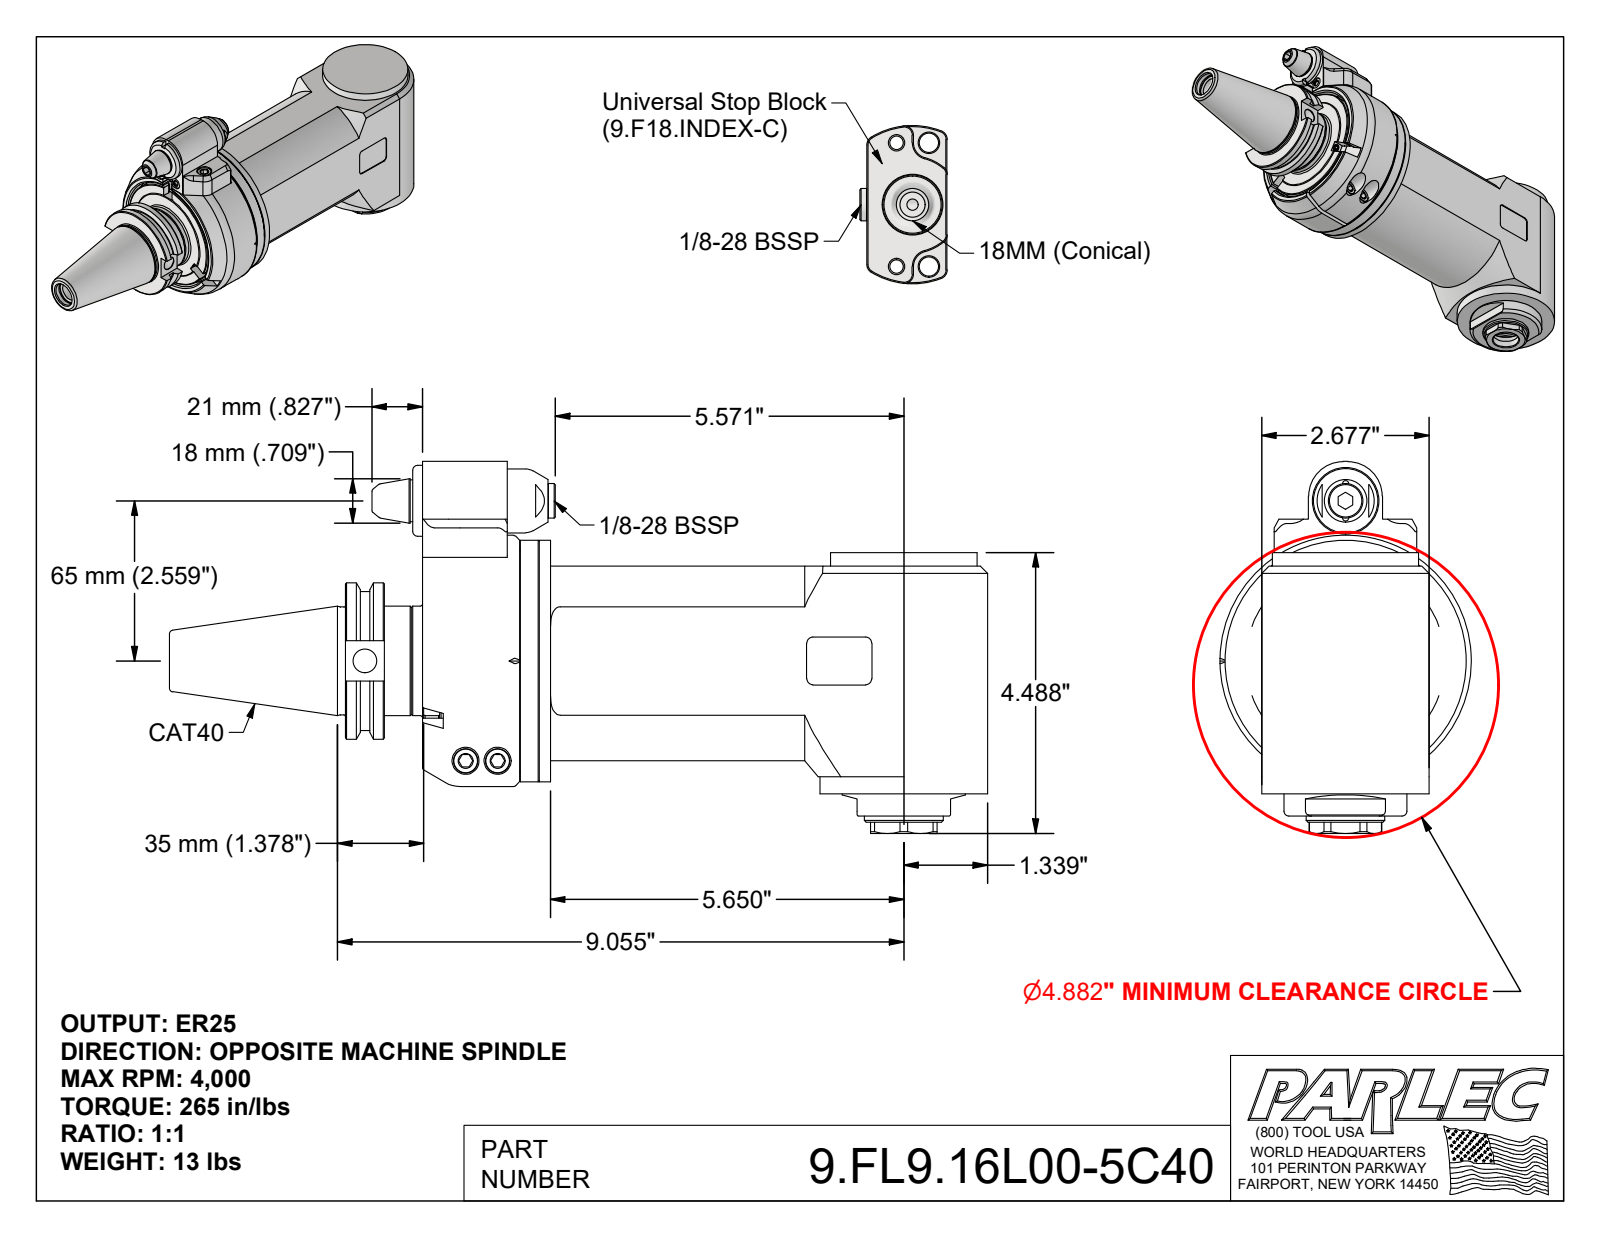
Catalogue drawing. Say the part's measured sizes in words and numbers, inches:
The part is named "9.FL9.16L00-5C40; 9_GA15C_446 (EVO, Type 1, Cat40, 65mm, conical); 9FA636000; VTCEI_M6X30 (+8 more)". Its 3-D file was written by "Autodesk Inventor 2022 (AUTOMOTIVE_DESIGN)". It is 27 solids with 739 faces: 312 planar, 205 cylindrical and 222 other. Overall it measures 13.081 by 5.945 by 4.016 inches. Its volume is 83.23 cubic inches and its surface area 291.4 square inches. Round holes: 7 of diameter 0.197, 6 of diameter 0.165, 4 of diameter 0.126, 4 of diameter 0.13, 4 of diameter 0.315, 3 of diameter 0.236, 2 of diameter 0.102, 2 of diameter 0.256, 2 of diameter 0.266, 2 of diameter 0.409, 2 of diameter 0.433, 2 of diameter 0.492. Round bosses or shafts: 5 of diameter 0.394, 4 of diameter 0.236, 4 of diameter 0.157, 2 of diameter 0.866, 2 of diameter 0.709, 2 of diameter 0.472, 2 of diameter 0.197, 1 of diameter 4.016. Partial cylindrical surfaces (rounded edges, fillets, slot ends): 14 of radius 0.039, 6 of radius 0.118, 4 of radius 0.098, 4 of radius 0.157, 2 of radius 0.02, 2 of radius 0.315, 2 of radius 0.551, 1 of radius 0.581. The main face-to-face distances are 2.677, 0.276, 0.02, 0.138, 0.492, 0.079, 0.217, 1.555, 1.28, 1.26. The hole center spacings are 0.325, 0.459, 0.276, 0.472, 0.504, 0.65, 0.74, 0.838.
